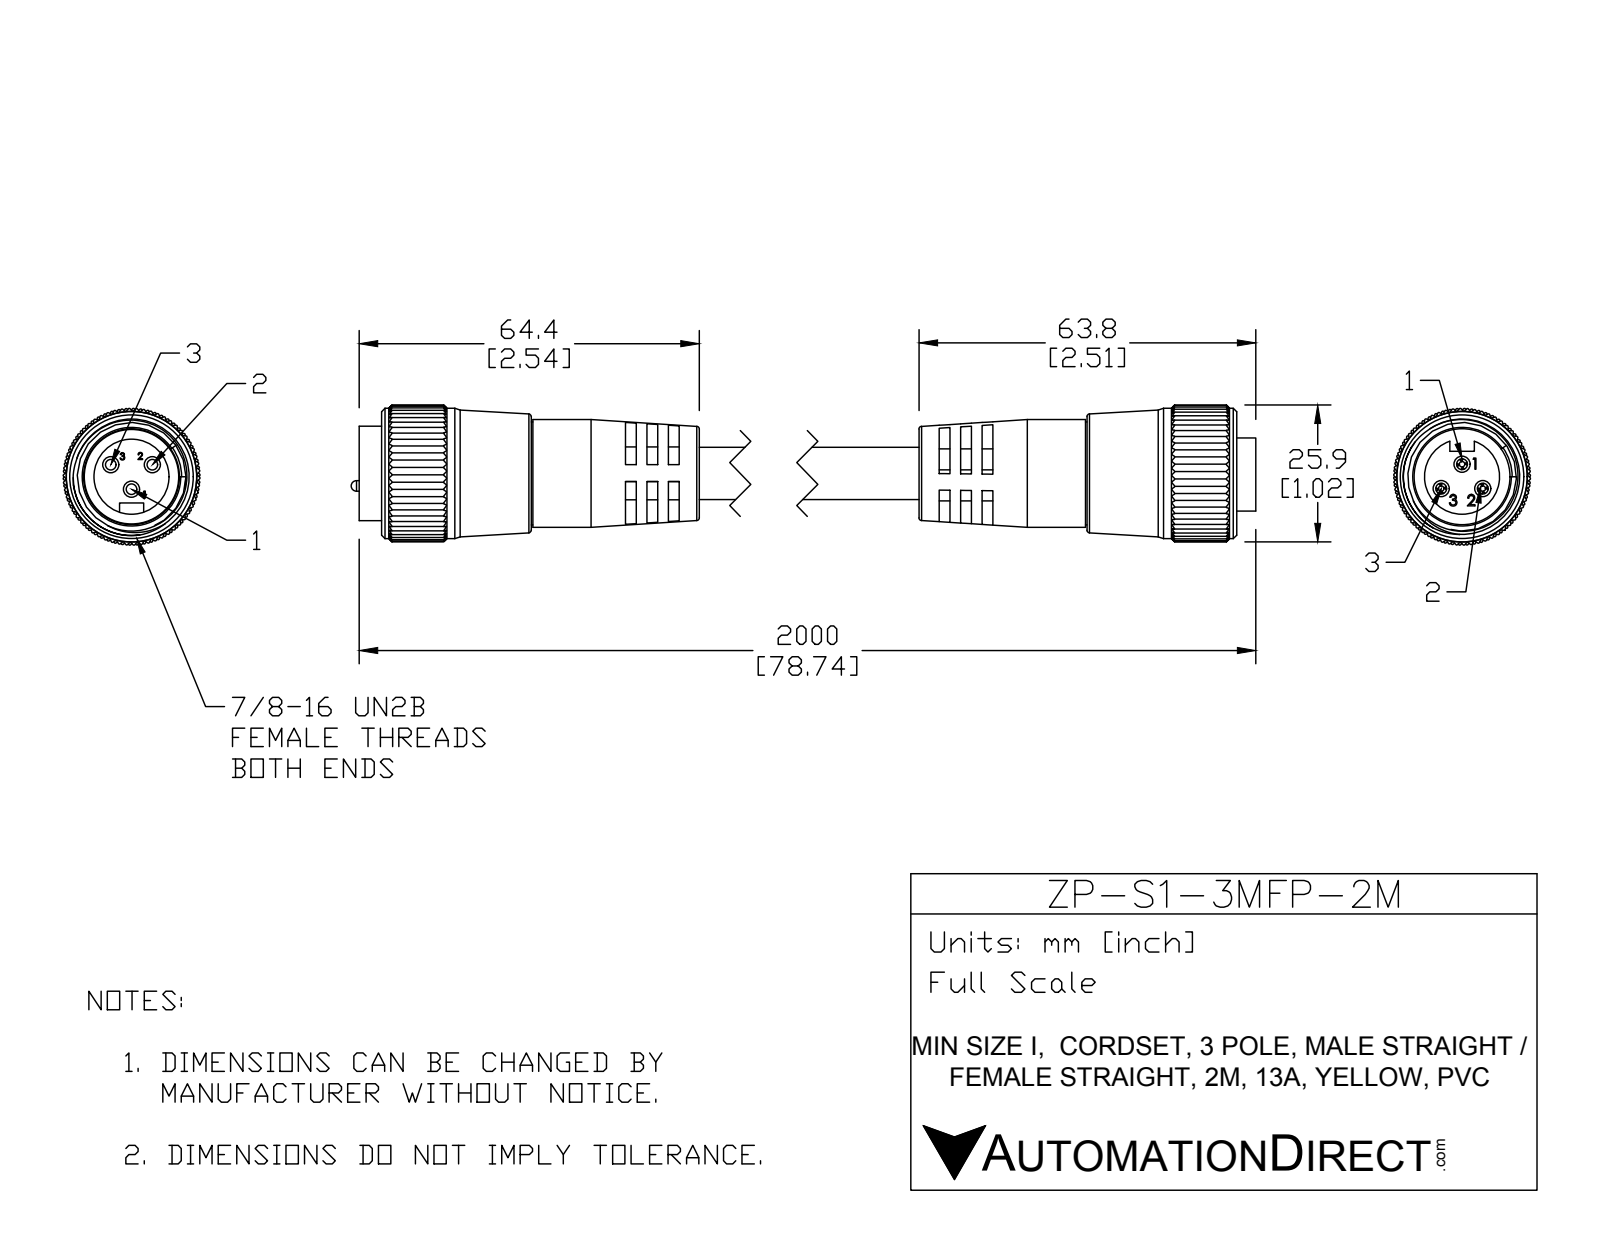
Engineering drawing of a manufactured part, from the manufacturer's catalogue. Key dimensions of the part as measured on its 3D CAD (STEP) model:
Part name (STEP PRODUCT): ZP-S1-3MFP-2M
STEP written by: SolidWorks 2015 (AUTOMOTIVE_DESIGN)
Units: millimetres
Bodies: 7 solids, 1099 faces (389 planar, 618 cylindrical, 92 other)
Overall size (bounding box): 229.66 × 25.84 × 25.83
Volume: 50 808 mm³ · Surface area: 23 333 mm²
Round holes (diameter × count): ⌀3.05 ×3, ⌀19.96 ×1, ⌀20.45 ×1, ⌀21 ×1
Round bosses / shafts (diameter × count): ⌀3.05 ×3, ⌀2 ×3, ⌀24.68 ×1, ⌀20.4 ×1, ⌀19.5 ×1, ⌀17.88 ×1, ⌀14.22 ×1, ⌀9.91 ×1
Partial cylindrical surfaces — rounded edges, fillets, slot ends (radius × count): R0.25 ×165, R2.29 ×1, R5.25 ×1, R12.93 ×1
Main face-to-face distances: 2, 4.02, 117.68, 113.65, 4.03, 125.74, 59.84, 4.04, 121.7, 121.72
Hole centre spacings: 6.07, 2.36, 4.53, 4.54, 7.87
